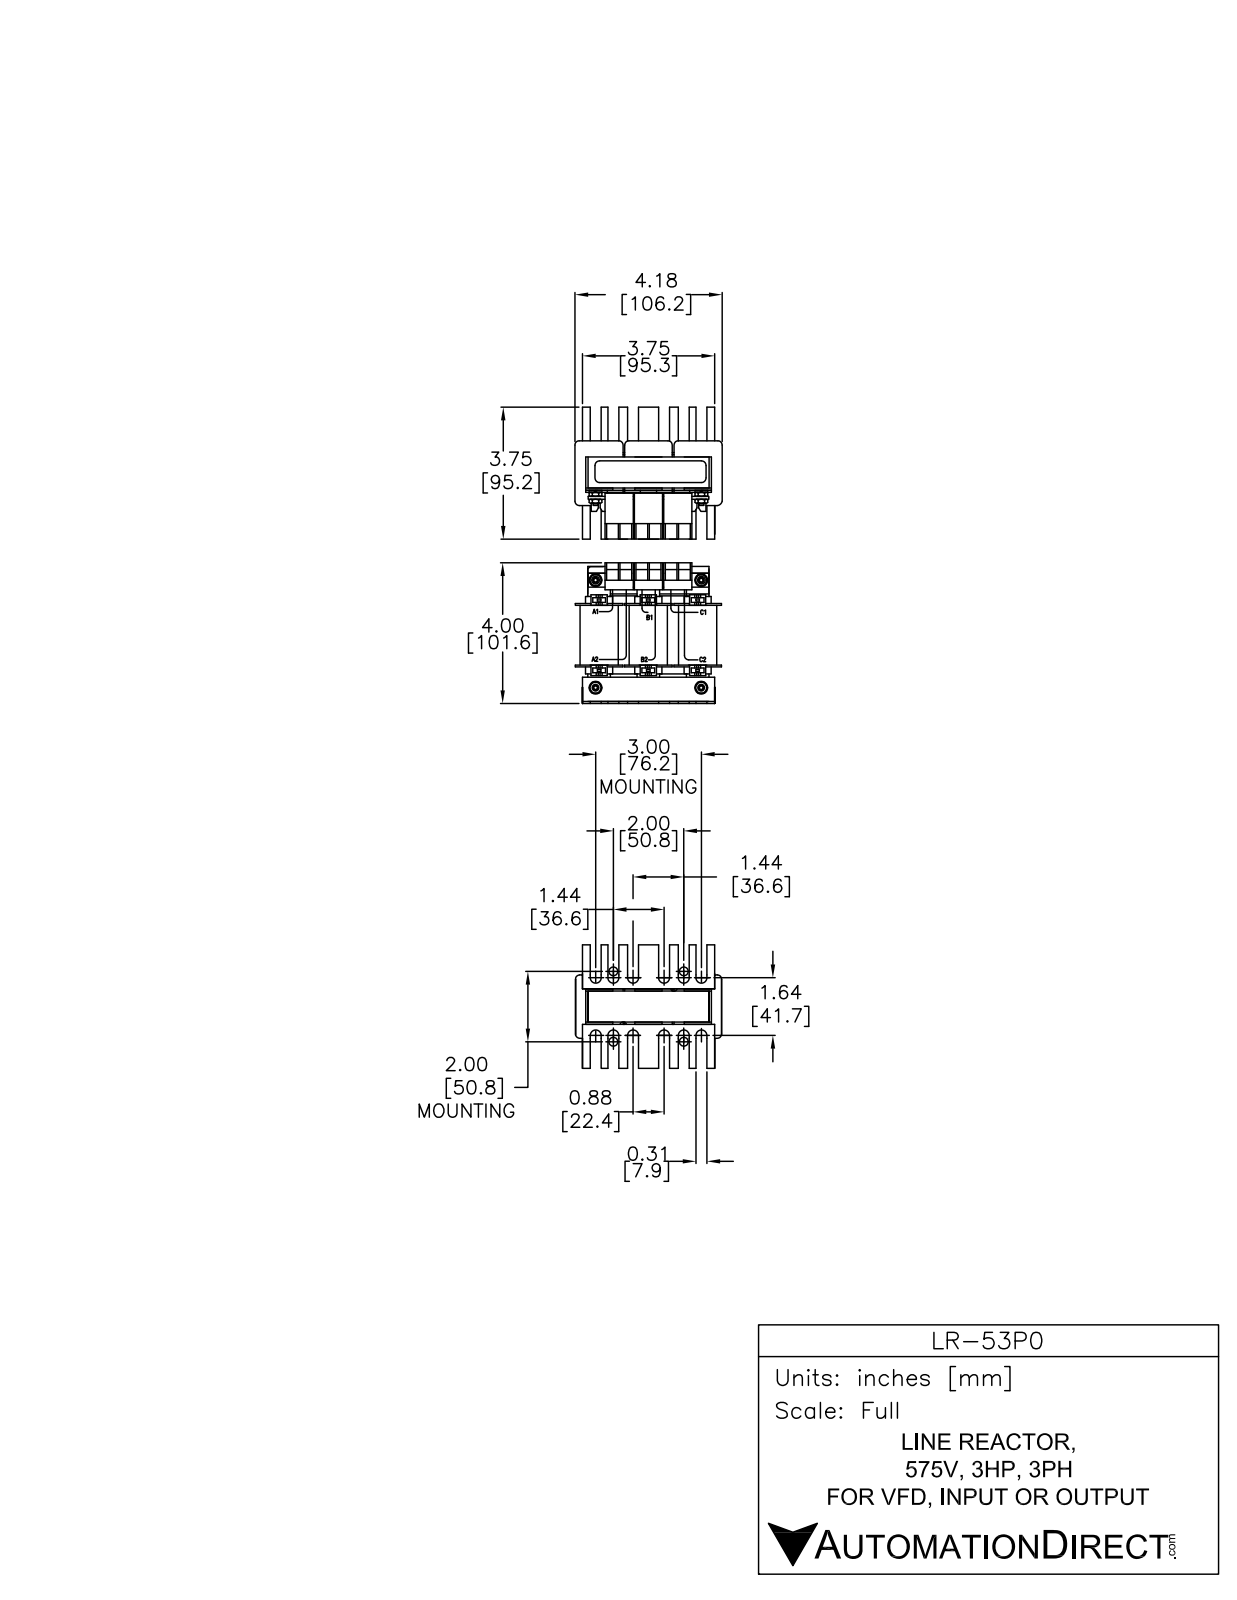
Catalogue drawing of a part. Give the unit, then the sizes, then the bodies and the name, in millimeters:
Units: millimetres
Overall size (bounding box): 105.25 × 98.41 × 89.25
Round bosses / shafts (diameter × count): ⌀7.75 ×4, ⌀3.5 ×4
Partial cylindrical surfaces — rounded edges, fillets, slot ends (radius × count): R4 ×50, R1.82 ×24, R8 ×12, R3 ×6, R0.86 ×3, R1.25 ×2
Main face-to-face distances: 5, 21.5, 2.75, 51, 26.25, 26.5, 7.5, 29, 71, 2.5
Volume: 272 326 mm³ · Surface area: 99 223 mm²
Bodies: 17 solids, 941 faces (743 planar, 198 cylindrical, 0 other)
Part name (STEP PRODUCT): LR-53P0
STEP written by: SolidWorks 2011 (AUTOMOTIVE_DESIGN)
